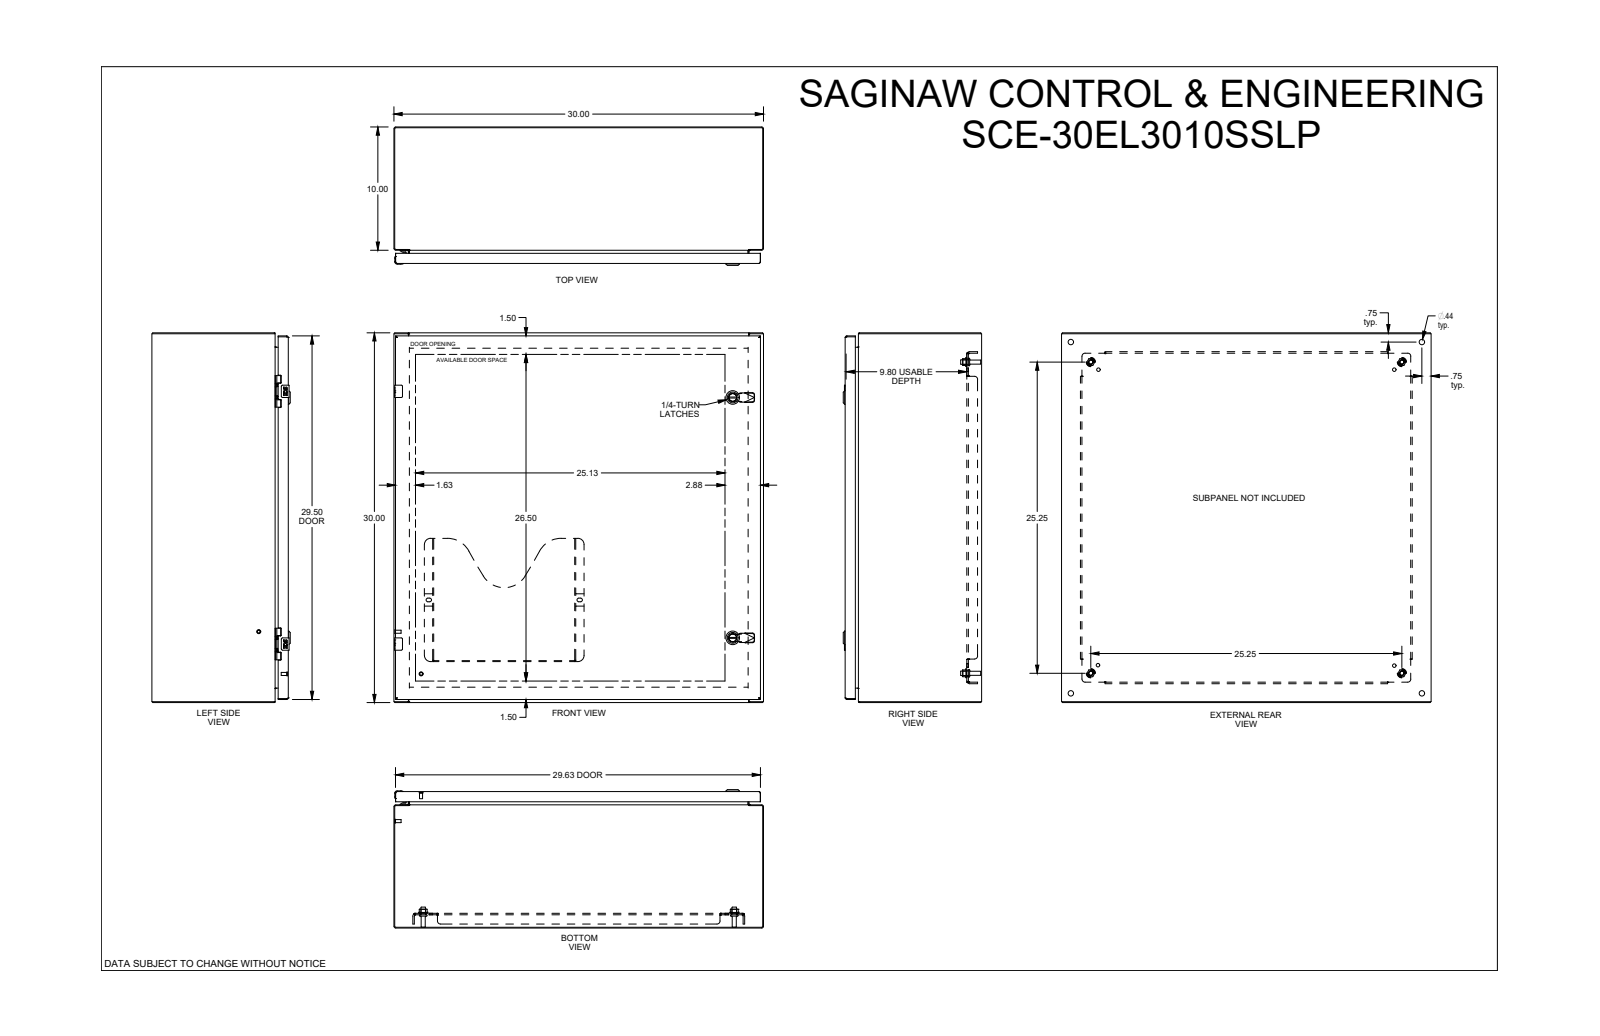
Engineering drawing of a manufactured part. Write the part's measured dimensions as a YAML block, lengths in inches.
part_name: "SCE-30EL3010SSLP"
step_written_by: "SolidWorks 2019 (CONFIG_CONTROL_DESIGN)"
units: inches
bodies: {solids: 0, faces: 2838, planar: 1307, cylindrical: 759, other: 772}
overall_size: [30, 30, 11.23]
round_holes:
  - {diameter: 0.172, count: 4}
  - {diameter: 0.205, count: 4}
  - {diameter: 0.244, count: 4}
  - {diameter: 0.266, count: 4}
  - {diameter: 0.281, count: 4}
  - {diameter: 0.367, count: 4}
  - {diameter: 0.437, count: 4}
  - {diameter: 0.5, count: 4}
  - {diameter: 0.375, count: 3}
  - {diameter: 0.156, count: 2}
  - {diameter: 0.197, count: 2}
  - {diameter: 0.218, count: 2}
round_bosses_or_shafts:
  - {diameter: 0.17, count: 6}
  - {diameter: 0.366, count: 4}
  - {diameter: 0.332, count: 4}
  - {diameter: 0.25, count: 4}
  - {diameter: 0.248, count: 4}
  - {diameter: 0.196, count: 3}
  - {diameter: 1.102, count: 2}
  - {diameter: 0.866, count: 2}
partial_cylinders:
  - {radius: 0.012, count: 56}
  - {radius: 0.01, count: 28}
  - {radius: 0.015, count: 28}
  - {radius: 0.04, count: 23}
  - {radius: 0.02, count: 20}
  - {radius: 0.07, count: 14}
  - {radius: 0.029, count: 12}
  - {radius: 0.145, count: 10}
face_to_face_distances: [0.075, 29.925, 0.075, 10.923, 10.998, 11.073, 10.998, 1.2, 9.873, 0.125]
hole_center_spacings: [20.5, 0.985, 26.352, 26.924, 24.639, 0.02, 0.875, 4.493]
